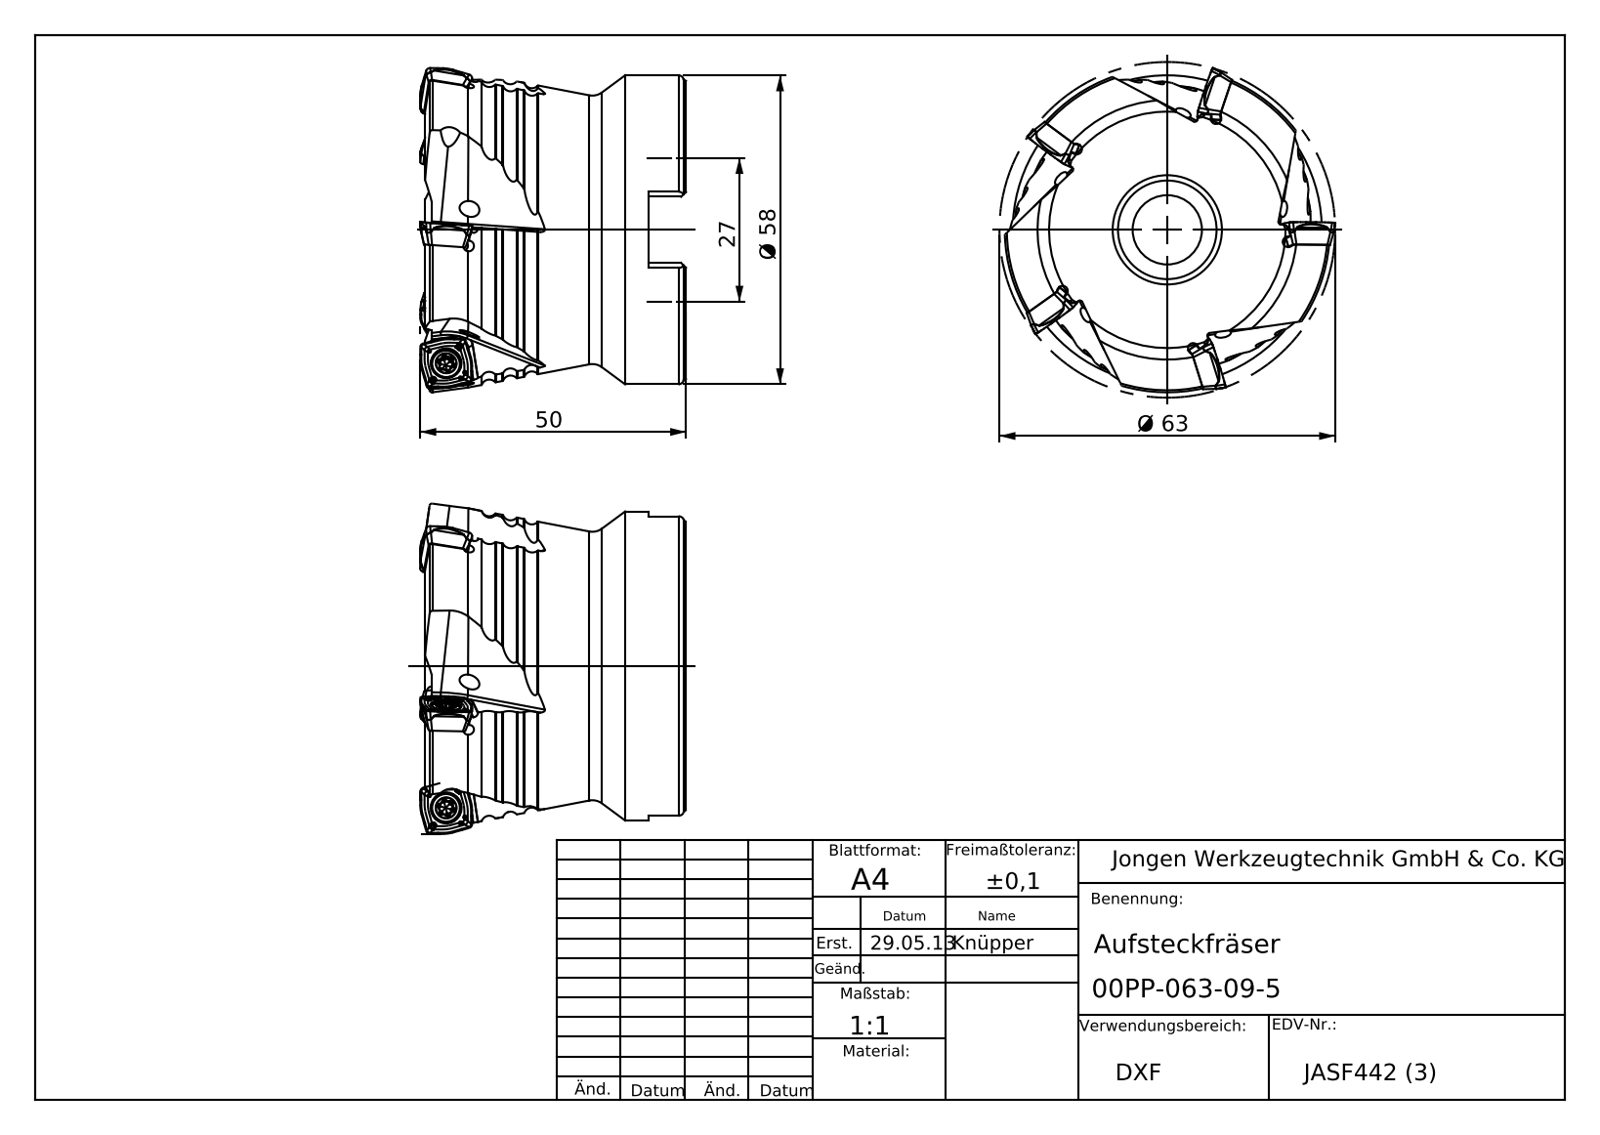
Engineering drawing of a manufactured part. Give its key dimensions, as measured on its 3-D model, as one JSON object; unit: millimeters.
{"part_name": "00PP-063-09-5", "step_written_by": "SolidWorks 2013 (AUTOMOTIVE_DESIGN)", "units": "millimeters", "bodies": {"solids": 1, "faces": 226, "planar": 74, "cylindrical": 46, "other": 106}, "overall_size": [62.98, 62.98, 50.06], "volume_mm3": 99223, "surface_area_mm2": 20158, "round_holes": [[3, 5], [13, 1], [18.5, 1], [26.8, 1], [27.15, 1], [27.3, 1]], "round_bosses_or_shafts": [[58, 1]], "partial_cylinders_radius": [[0.5, 10], [0.8, 10], [1, 10], [2, 5]], "face_to_face_distances": [47.75, 7, 40.75, 12.4, 34, 27, 13.75, 22, 15, 12]}
